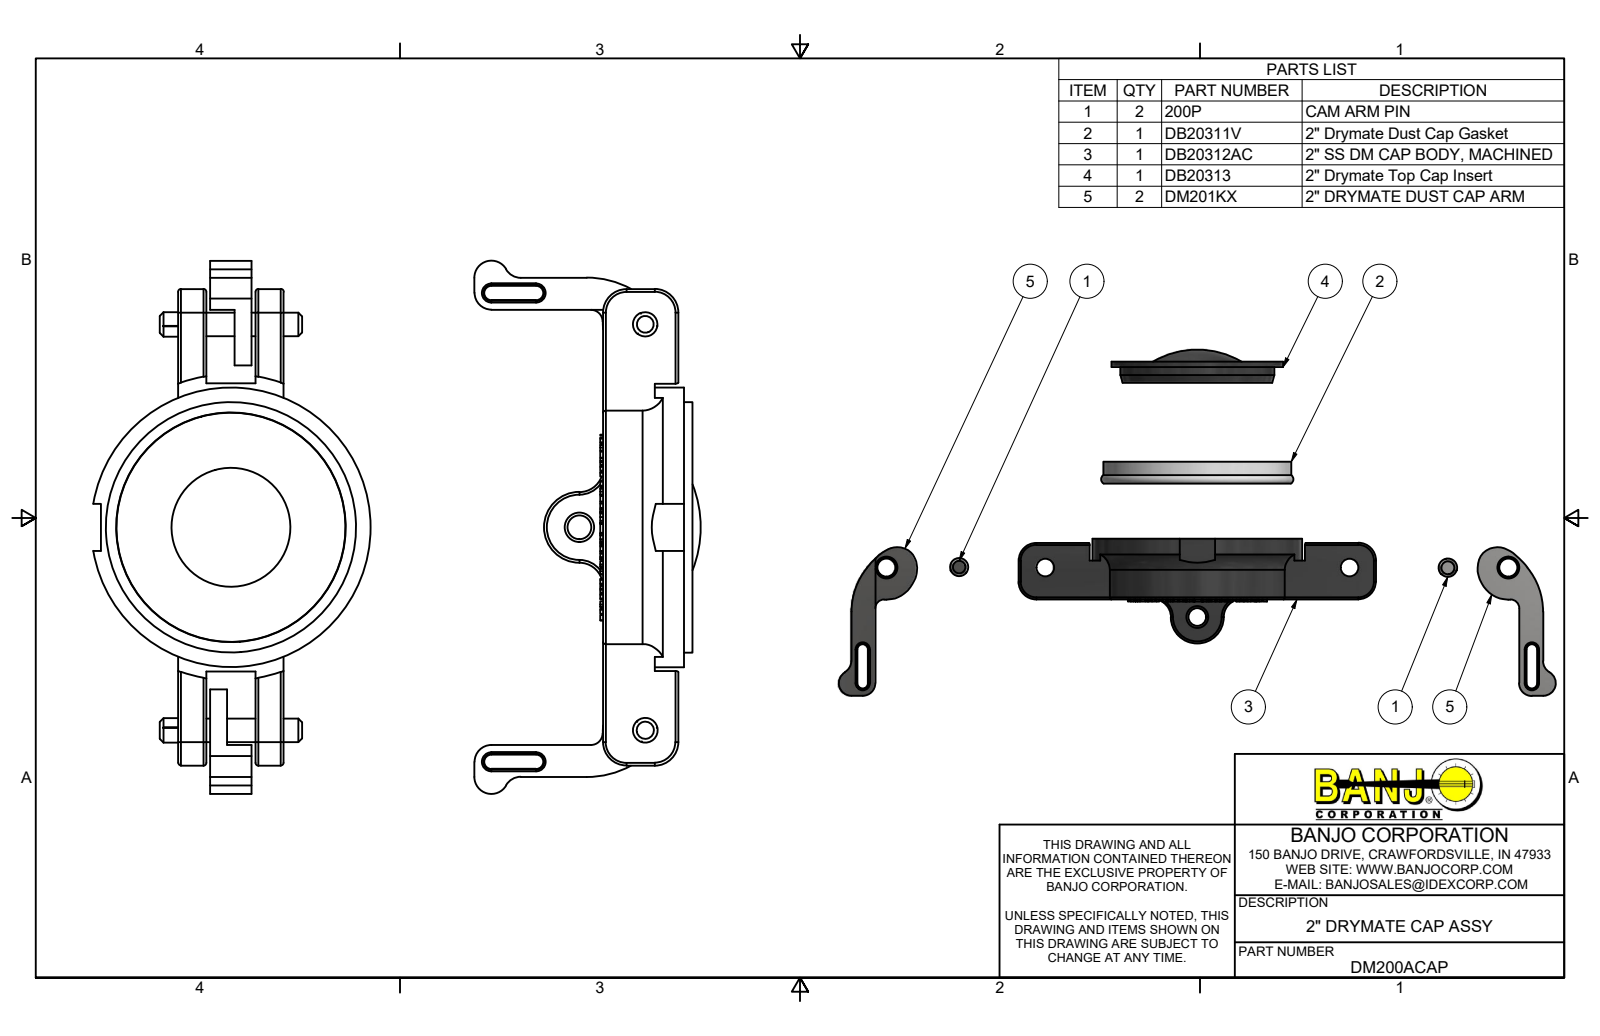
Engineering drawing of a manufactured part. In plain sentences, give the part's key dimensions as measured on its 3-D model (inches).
The part is named "DM200ACAP; DB20312AC; DB20312AX; DB20311V (+3 more)". Its 3-D file was written by "Autodesk Inventor 2019 (AUTOMOTIVE_DESIGN)". It is 7 solids with 668 faces: 377 planar, 106 cylindrical and 185 other. Overall it measures 5.66 by 2.949 by 2.403 inches. Its volume is 5.952 cubic inches and its surface area 72.67 square inches. Round holes: 3 of diameter 0.125, 3 of diameter 0.25, 2 of diameter 0.256, 1 of diameter 2.188, 1 of diameter 2.438, 1 of diameter 2.66. Round bosses or shafts: 3 of diameter 0.28, 2 of diameter 0.26, 2 of diameter 0.249, 1 of diameter 2.97, 1 of diameter 2.72, 1 of diameter 2.43, 1 of diameter 2.18. Partial cylindrical surfaces (rounded edges, fillets, slot ends): 20 of radius 0.03, 6 of radius 0.18, 6 of radius 0.25, 4 of radius 0.075, 2 of radius 0.124, 2 of radius 0.983, 1 of radius 0.375, 1 of radius 1.045. The main face-to-face distances are 0.298, 0.822, 0.225, 0.78, 0.64, 0.865, 0.34, 0.042, 0.482, 1.12. The hole center spacings are 0.95, 1.645, 2.266, 1.646, 4.31.
